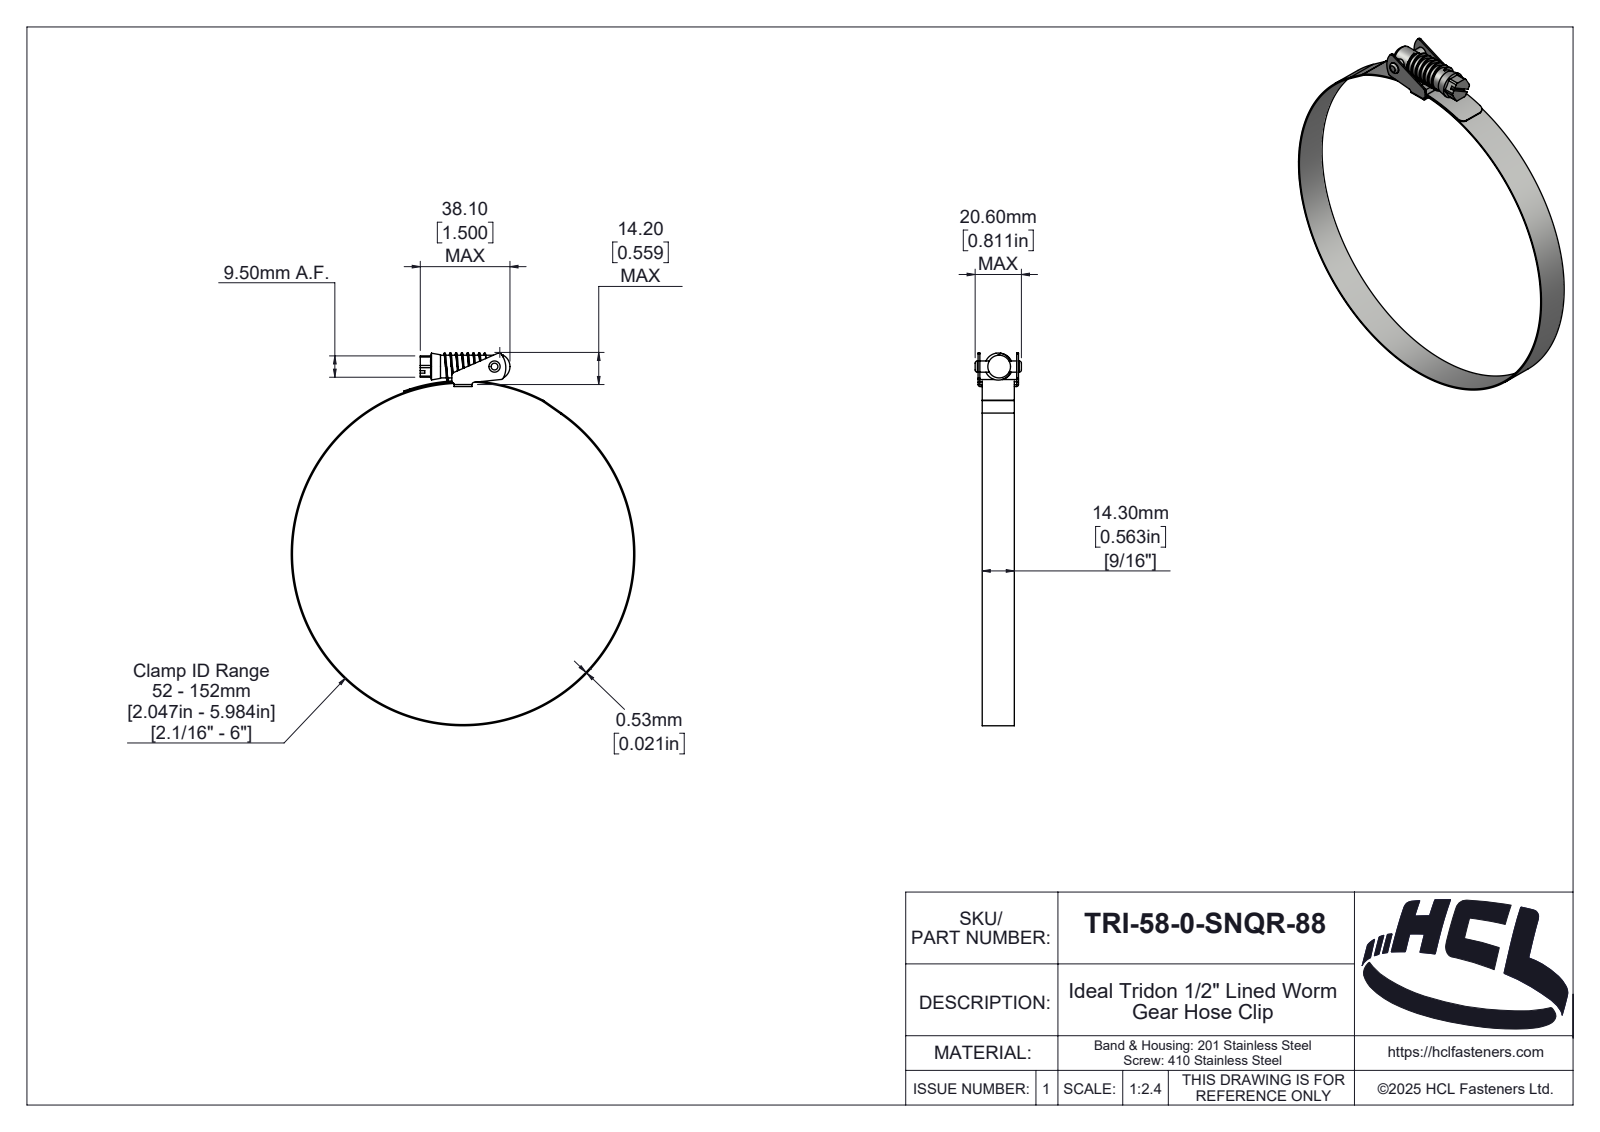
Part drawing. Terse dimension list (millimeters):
name: TRI-58-0-SNQR-88
written by: SolidWorks 2025 (AUTOMOTIVE_DESIGN)
unit: mm
bodies: 5 solids, 222 faces (44 planar, 112 cylindrical, 66 other)
size: 166.02 × 153.06 × 20.6
volume: 7 658 mm³; area: 18 967 mm²
holes: 1× ⌀5, 1× ⌀152
bosses: 1× ⌀153.06, 1× ⌀10.1
rounds: 11× R1, 2× R0.1, 2× R0.9, 2× R3, 1× R0.46, 1× R1.89, 1× R2, 1× R2.35
face distances: 0.8, 17.2, 1.85, 16.15, 1.05, 15.35, 14.3, 18, 16.4, 0.53
hole spacings: 84.57
